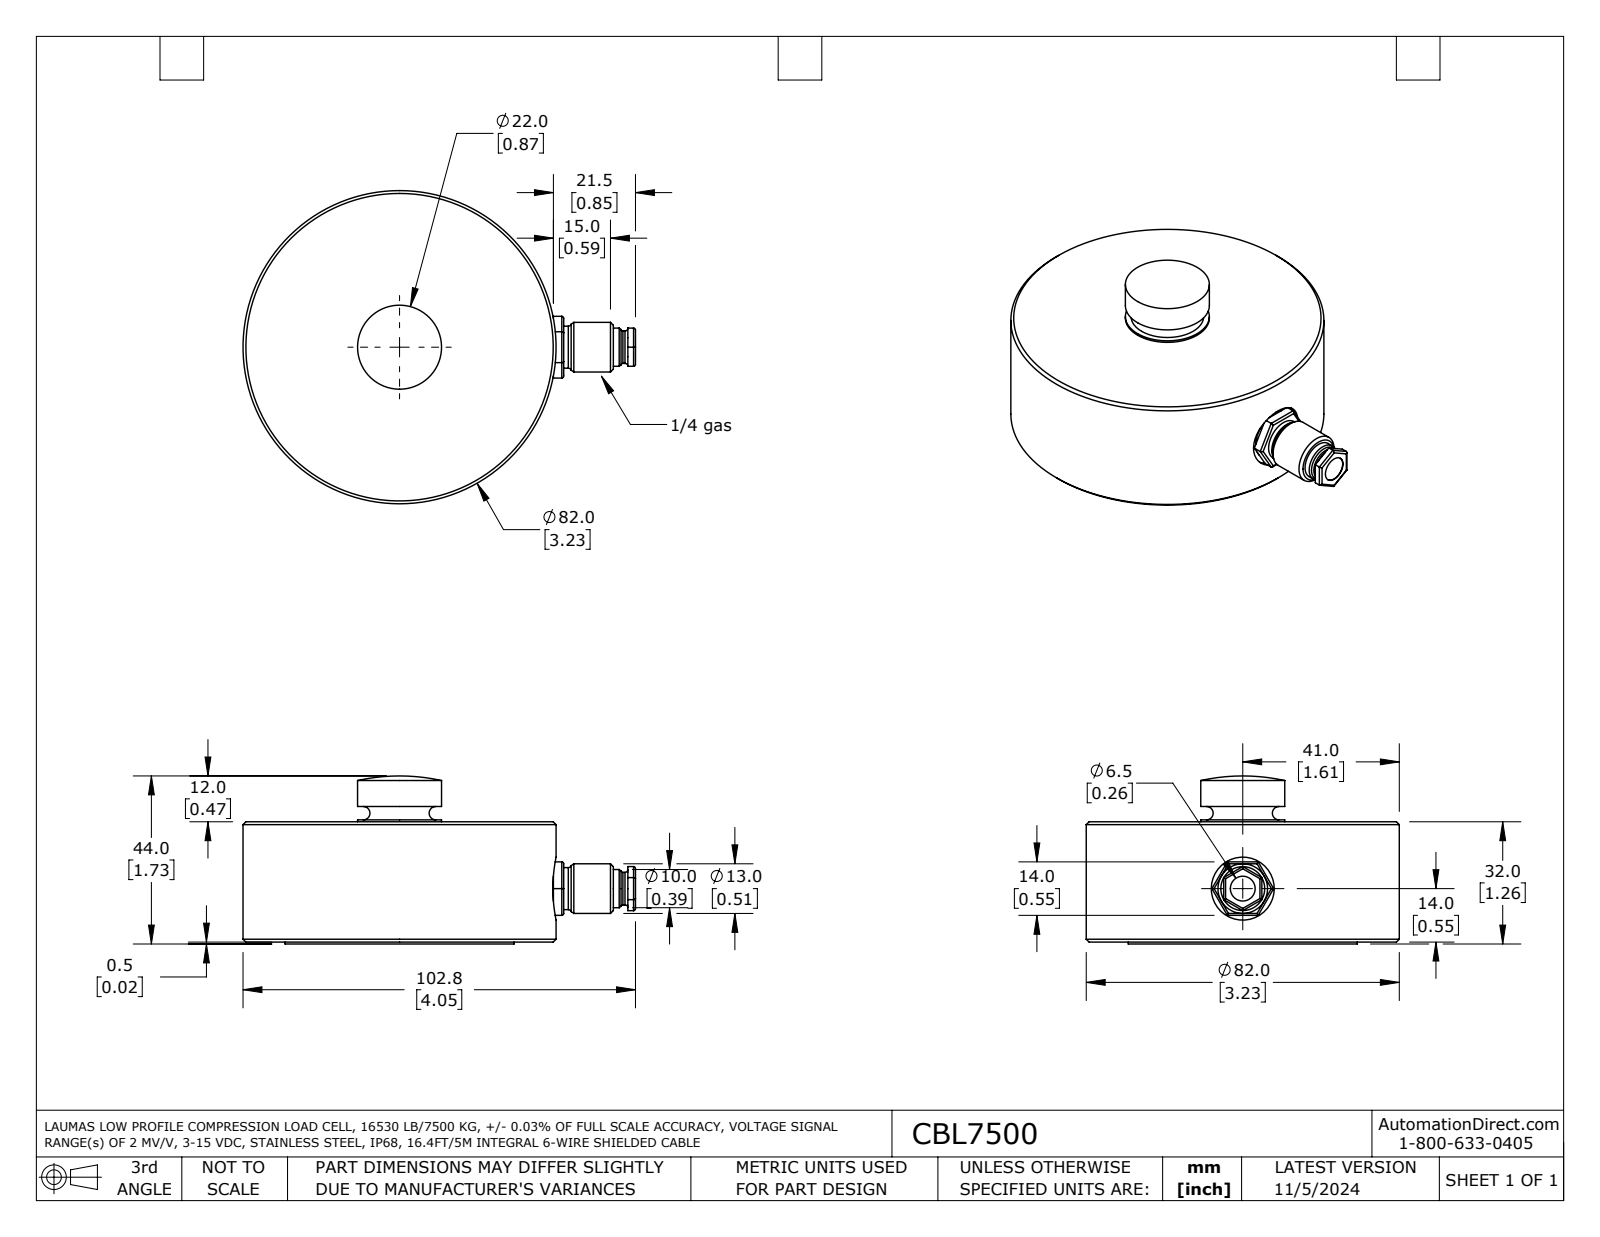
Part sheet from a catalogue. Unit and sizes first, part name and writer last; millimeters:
Units: millimetres
Overall size (bounding box): 102.8 × 82 × 44
Round holes (diameter × count): ⌀6.5 ×1, ⌀16.5 ×1, ⌀54.6 ×1
Round bosses / shafts (diameter × count): ⌀82 ×1, ⌀60 ×1, ⌀22 ×1, ⌀13.5 ×1, ⌀13 ×1, ⌀11 ×1, ⌀10 ×1, ⌀8.5 ×1
Partial cylindrical surfaces — rounded edges, fillets, slot ends (radius × count): R0.5 ×12
Main face-to-face distances: 30.8, 0.8, 31.5, 0.5, 32, 1.2, 3.5, 32.5, 31.2, 36
Volume: 170 800 mm³ · Surface area: 21 060 mm²
Bodies: 2 solids, 86 faces (31 planar, 36 cylindrical, 19 other)
Part name (STEP PRODUCT): CBL7500
STEP written by: SolidWorks 2021 (AUTOMOTIVE_DESIGN)
